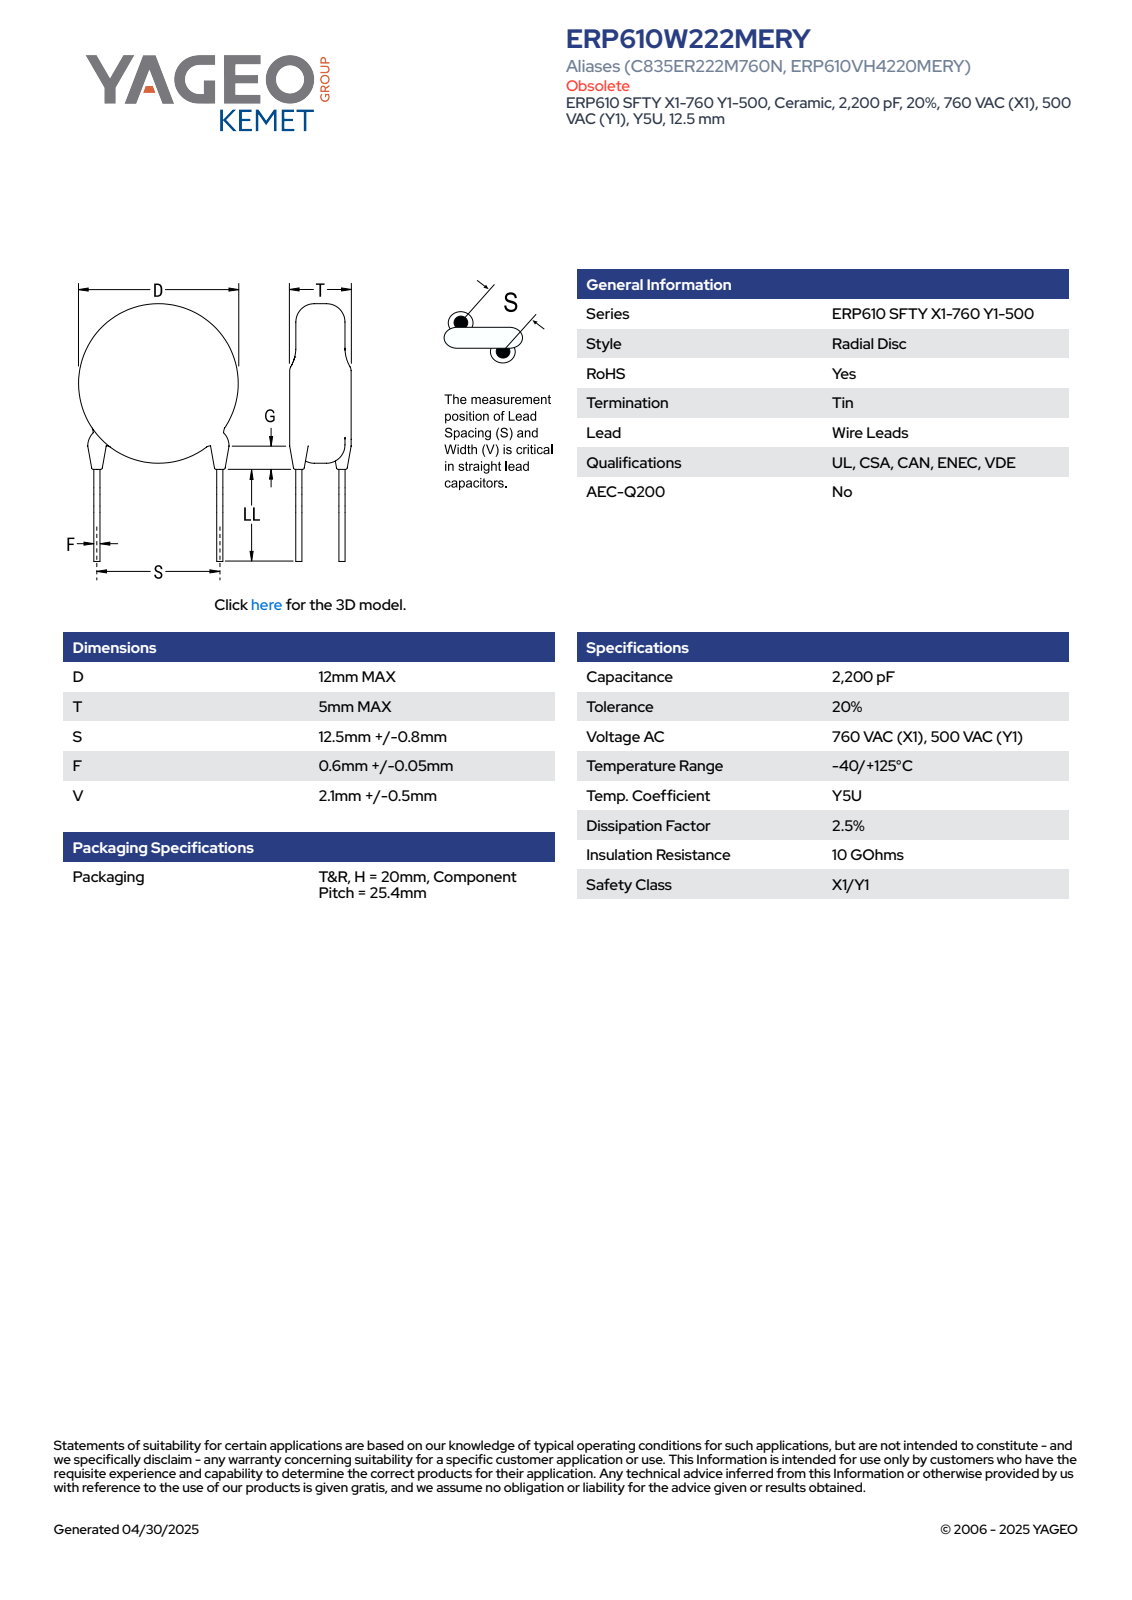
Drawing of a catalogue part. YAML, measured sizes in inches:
part_name: "CCD_KST_12X5_D12T5S12.5LL11F0.65G3V2.6"
step_written_by: "SolidWorks 2014 (AUTOMOTIVE_DESIGN)"
units: inches
bodies: {solids: 4, faces: 81, planar: 63, cylindrical: 6, other: 12}
overall_size: [0.913, 0.507, 0.197]
volume: 0.034
surface_area: 0.705
round_bosses_or_shafts:
  - {diameter: 0.026, count: 2}
  - {diameter: 0.472, count: 1}
face_to_face_distances: [0.197, 0.706, 0.648, 0.059, 0.016, 0.015, 0.24, 0.121, 0.174, 0.181]
